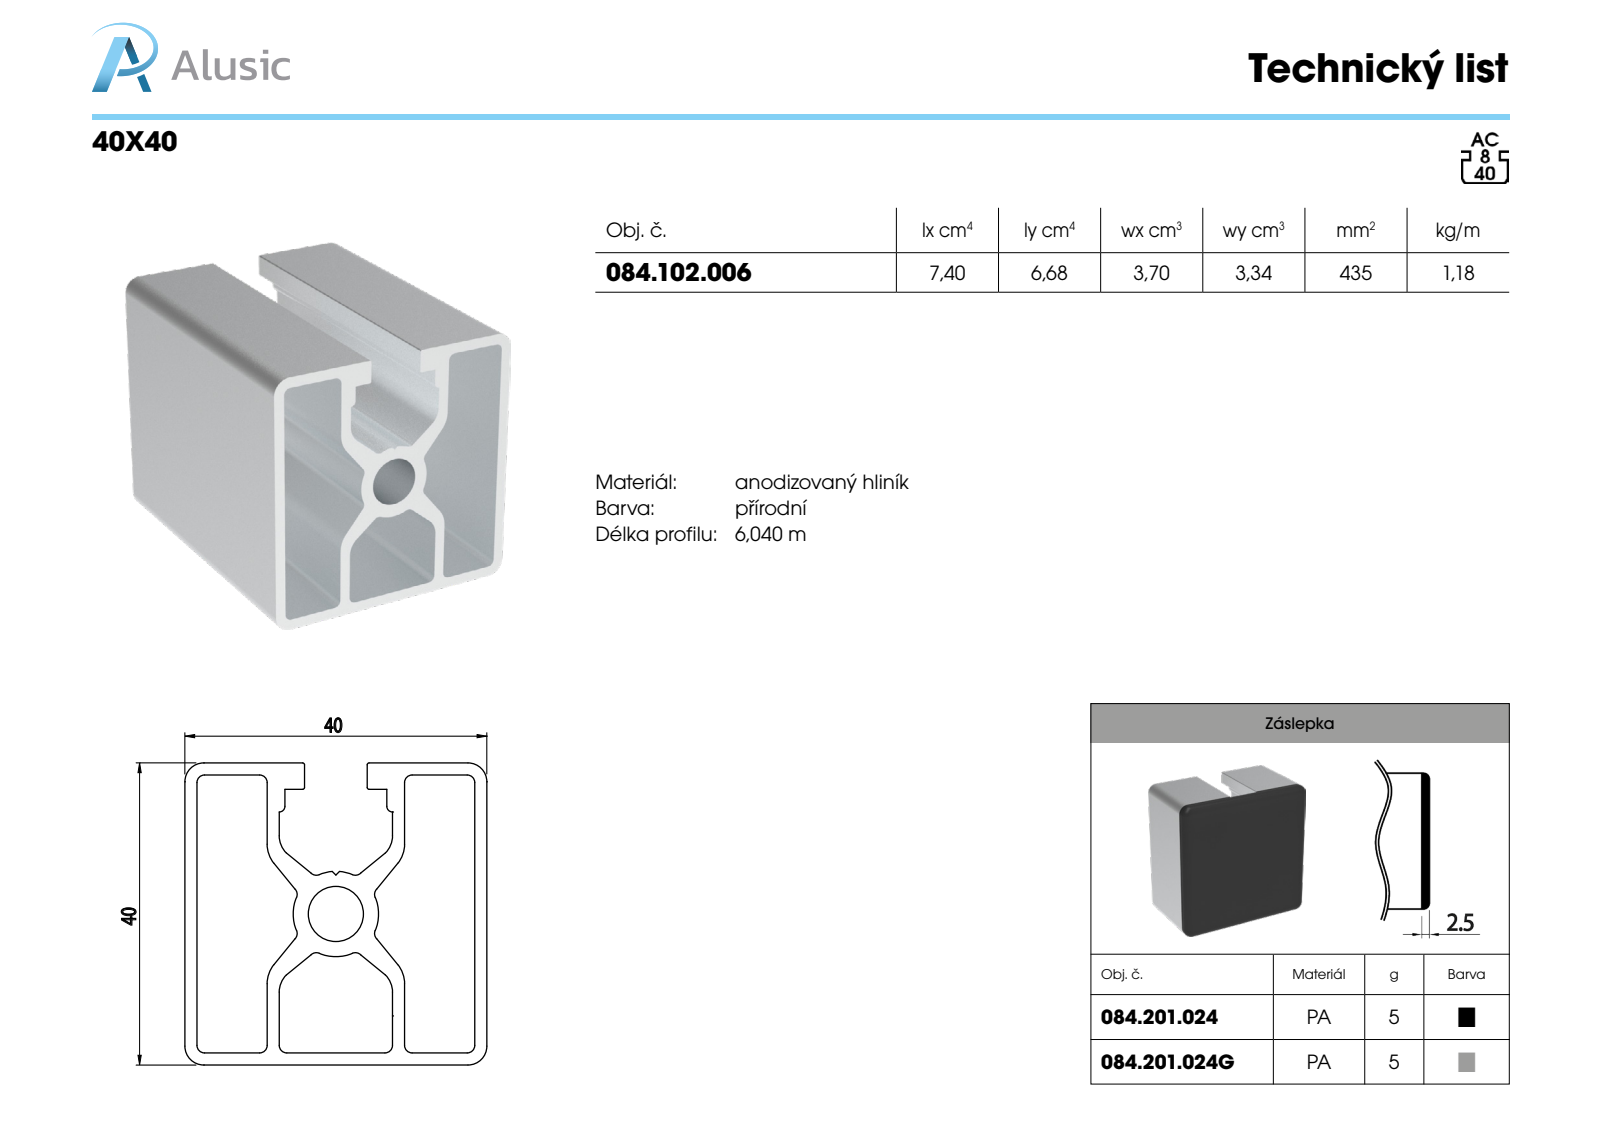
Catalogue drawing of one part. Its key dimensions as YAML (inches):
part_name: "084.102.006"
step_written_by: "SolidWorks 2011 (CONFIG_CONTROL_DESIGN)"
units: inches
bodies: {solids: 1, faces: 84, planar: 38, cylindrical: 46, other: 0}
overall_size: [3.937, 1.575, 1.575]
volume: 2.632
surface_area: 71.55
round_holes:
  - {diameter: 0.287, count: 1}
partial_cylinders:
  - {radius: 0.039, count: 18}
  - {radius: 0.01, count: 4}
  - {radius: 0.098, count: 4}
  - {radius: 0.126, count: 4}
  - {radius: 0.157, count: 4}
  - {radius: 0.03, count: 2}
  - {radius: 0.222, count: 1}
face_to_face_distances: [0.063, 1.512, 1.575, 0.429, 1.083, 1.449, 1.146, 0.366, 0.492, 1.02]
